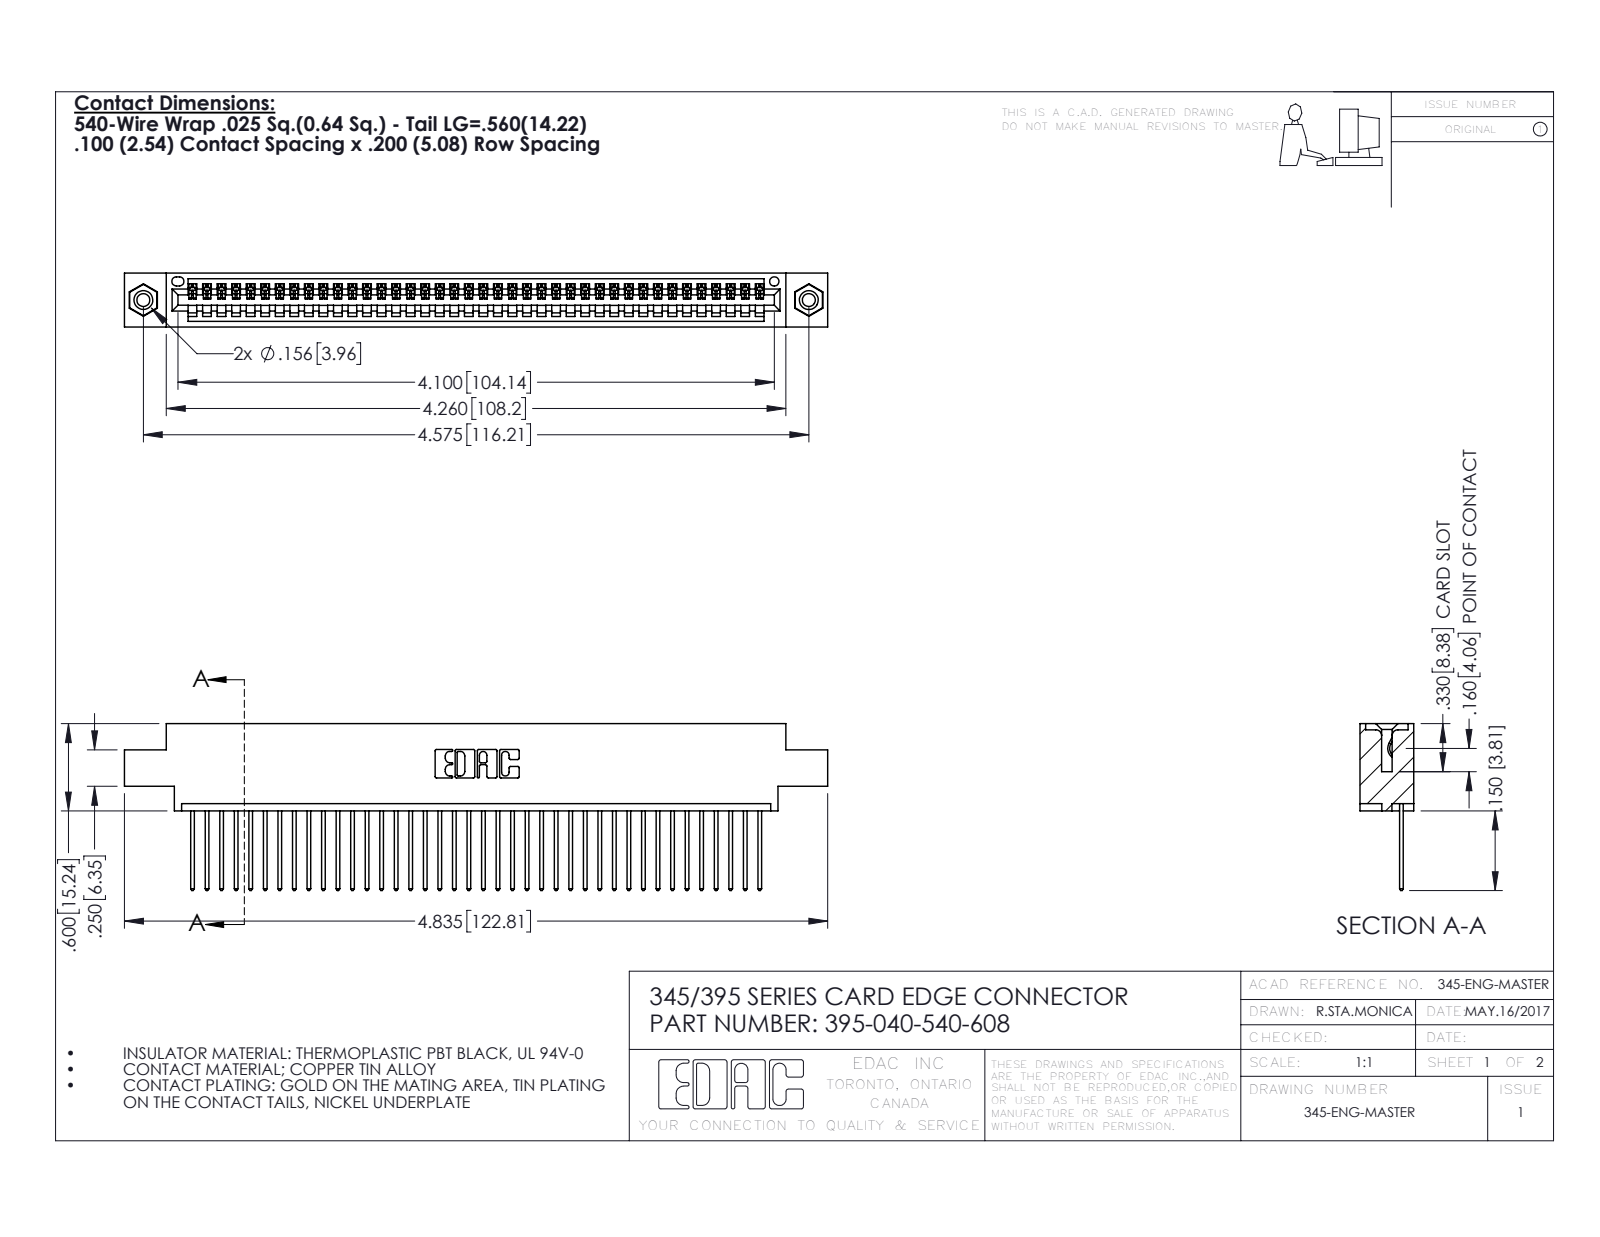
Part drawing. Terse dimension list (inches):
name: 345-250-001_345-250-003-102; 395-040-540-608; 345 Part_0.170 Offset - 0.156 Dia-TI; 345-292-001_345-293-140
written by: SolidWorks 2016 (CONFIG_CONTROL_DESIGN)
unit: in
bodies: 43 solids, 2510 faces (1716 planar, 778 cylindrical, 16 other)
size: 4.835 × 1.147 × 0.37
volume: 0.707 in³; area: 24.65 in²
holes: 2× ⌀0.089, 2× ⌀0.125, 2× ⌀0.156, 1× ⌀0.064
bosses: 2× ⌀0.155
rounds: 80× R0.006, 80× R0.01, 22× R0.01, 6× R0.007, 6× R0.031, 3× R0.026, 2× R0.031, 2× R0.04
face distances: 0.072, 0.298, 0.37, 0.098, 0.272, 0.025, 0.2, 0.225, 0.175, 0.149
hole spacings: 0.27, 4.339, 4.575
